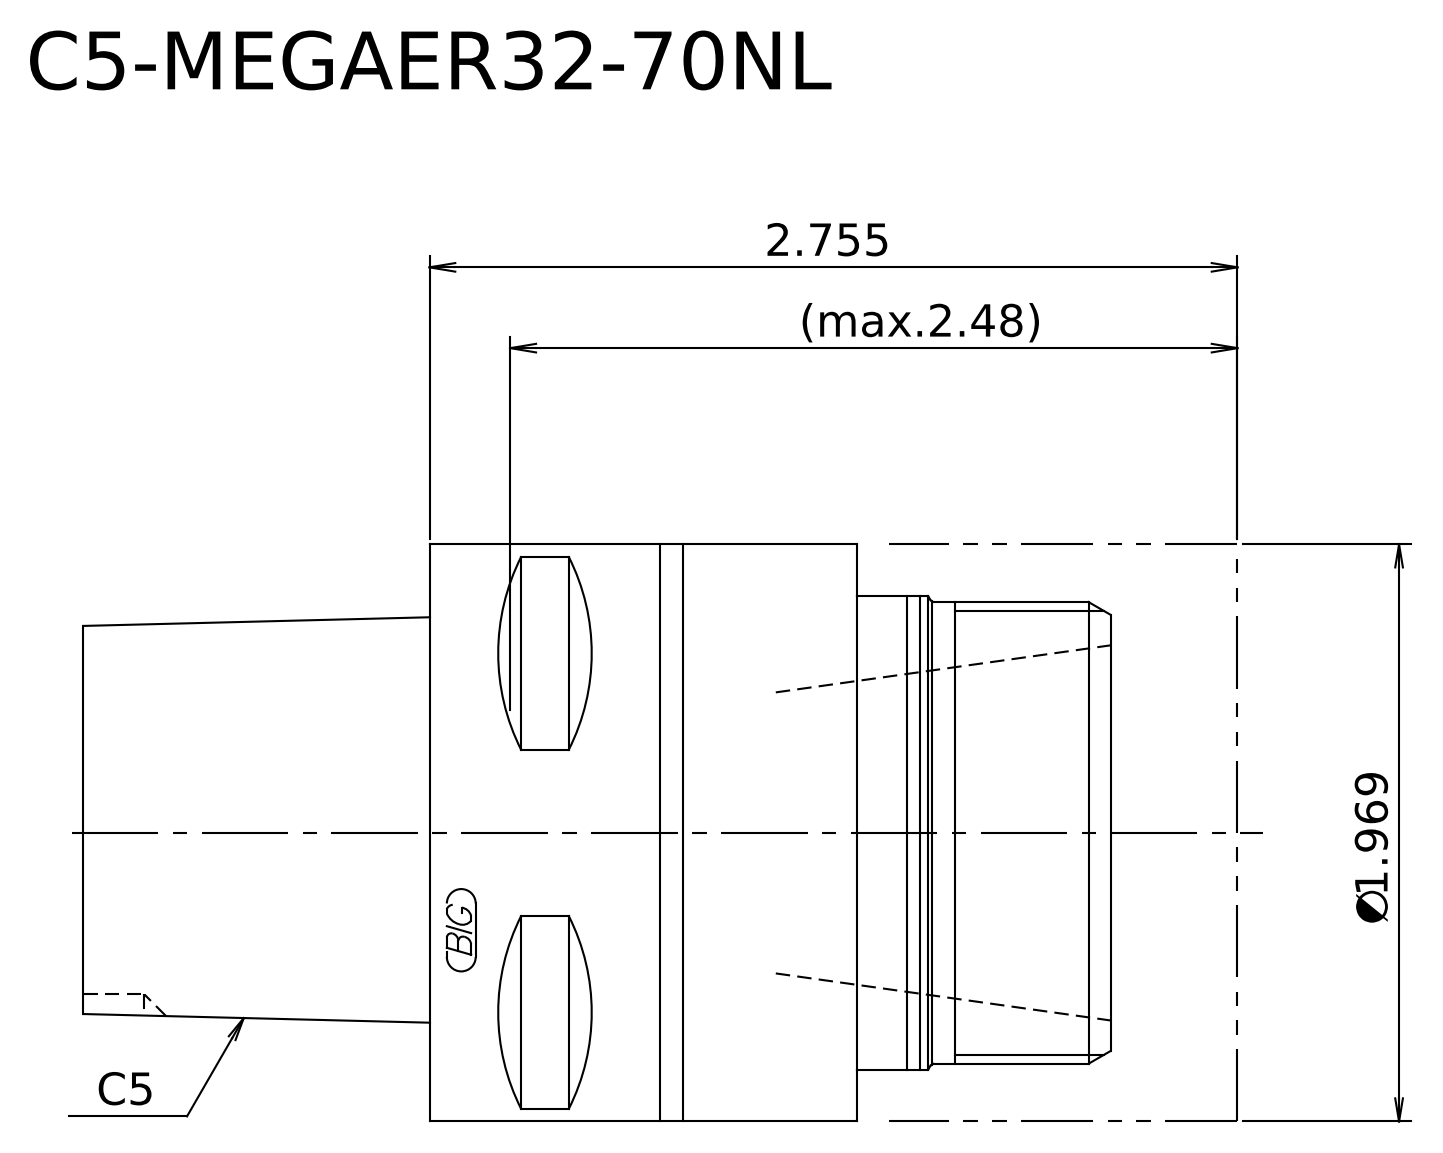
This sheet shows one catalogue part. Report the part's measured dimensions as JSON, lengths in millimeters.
{"step_written_by": "Kubotek KeyCreator 2011 V10.0.2 (22737) (automotive_design)", "units": "millimeters", "bodies": {"solids": 2, "faces": 13, "planar": 6, "cylindrical": 4, "other": 3}, "overall_size": [100, 50, 50], "volume_mm3": 187056, "surface_area_mm2": 24224, "round_bosses_or_shafts": [[50, 1], [41, 1], [40, 1]], "face_to_face_distances": [30.2, 11, 19.2, 70, 59, 39.8, 100, 89, 69.8, 30]}
